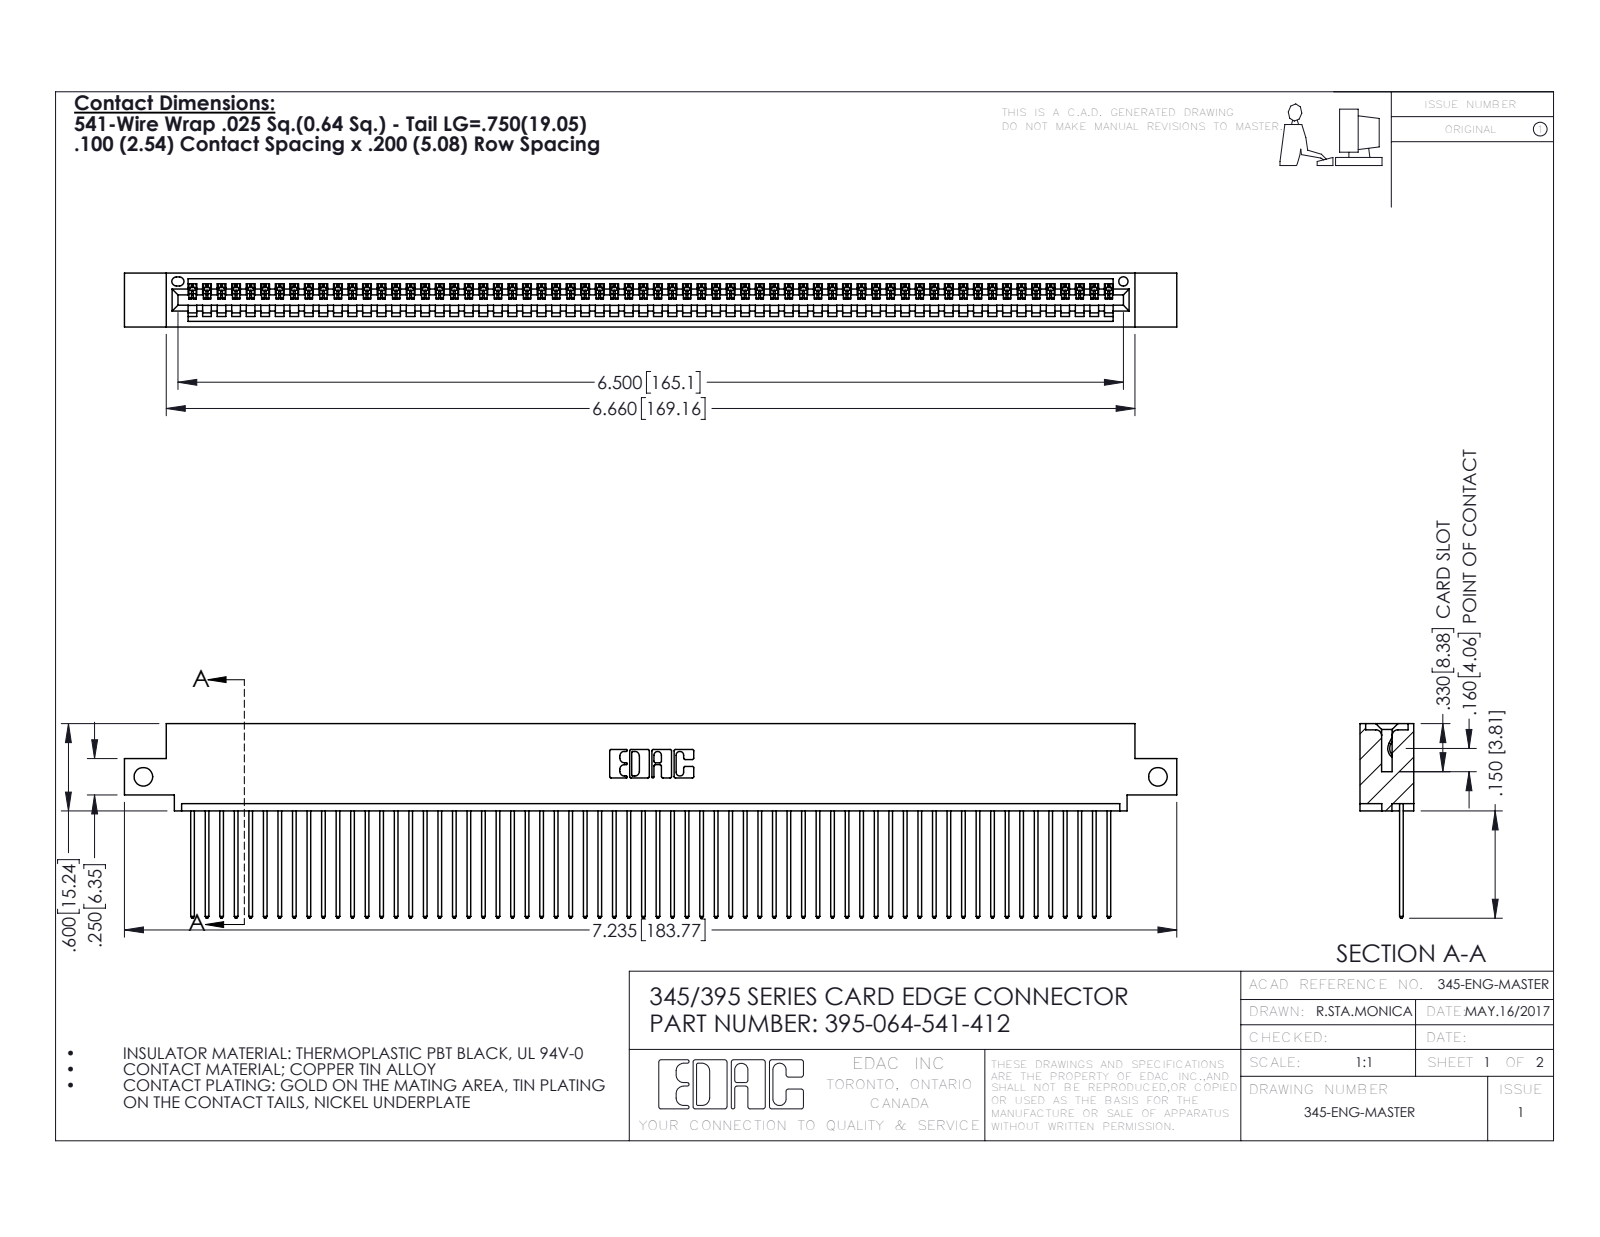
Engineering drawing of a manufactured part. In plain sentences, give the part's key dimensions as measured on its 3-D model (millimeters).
The part is named "395-064-541-412; 345-292-001_345-293-141; 345 Part_0.110 Offset - Side Mount". Its 3-D file was written by "SolidWorks 2016 (CONFIG_CONTROL_DESIGN)". It is 65 solids with 3842 faces: 2644 planar, 1198 cylindrical and 0 other. Overall it measures 183.8 by 34 by 9.4 millimeters. Its volume is 17 680 cubic millimeters and its surface area 24 980 square millimeters. Round holes: 2 of diameter 3.3, 1 of diameter 1.6. Partial cylindrical surfaces (rounded edges, fillets, slot ends): 128 of radius 0.2, 128 of radius 0.3, 22 of radius 0.3, 6 of radius 0.2, 6 of radius 0.8, 3 of radius 0.7, 2 of radius 0.8, 2 of radius 1. The main face-to-face distances are 1.8, 7.6, 2.5, 6.9, 0.6, 9.4, 5.1, 5.7, 3.8, 1.8. The hole center spacings are 177.2.
